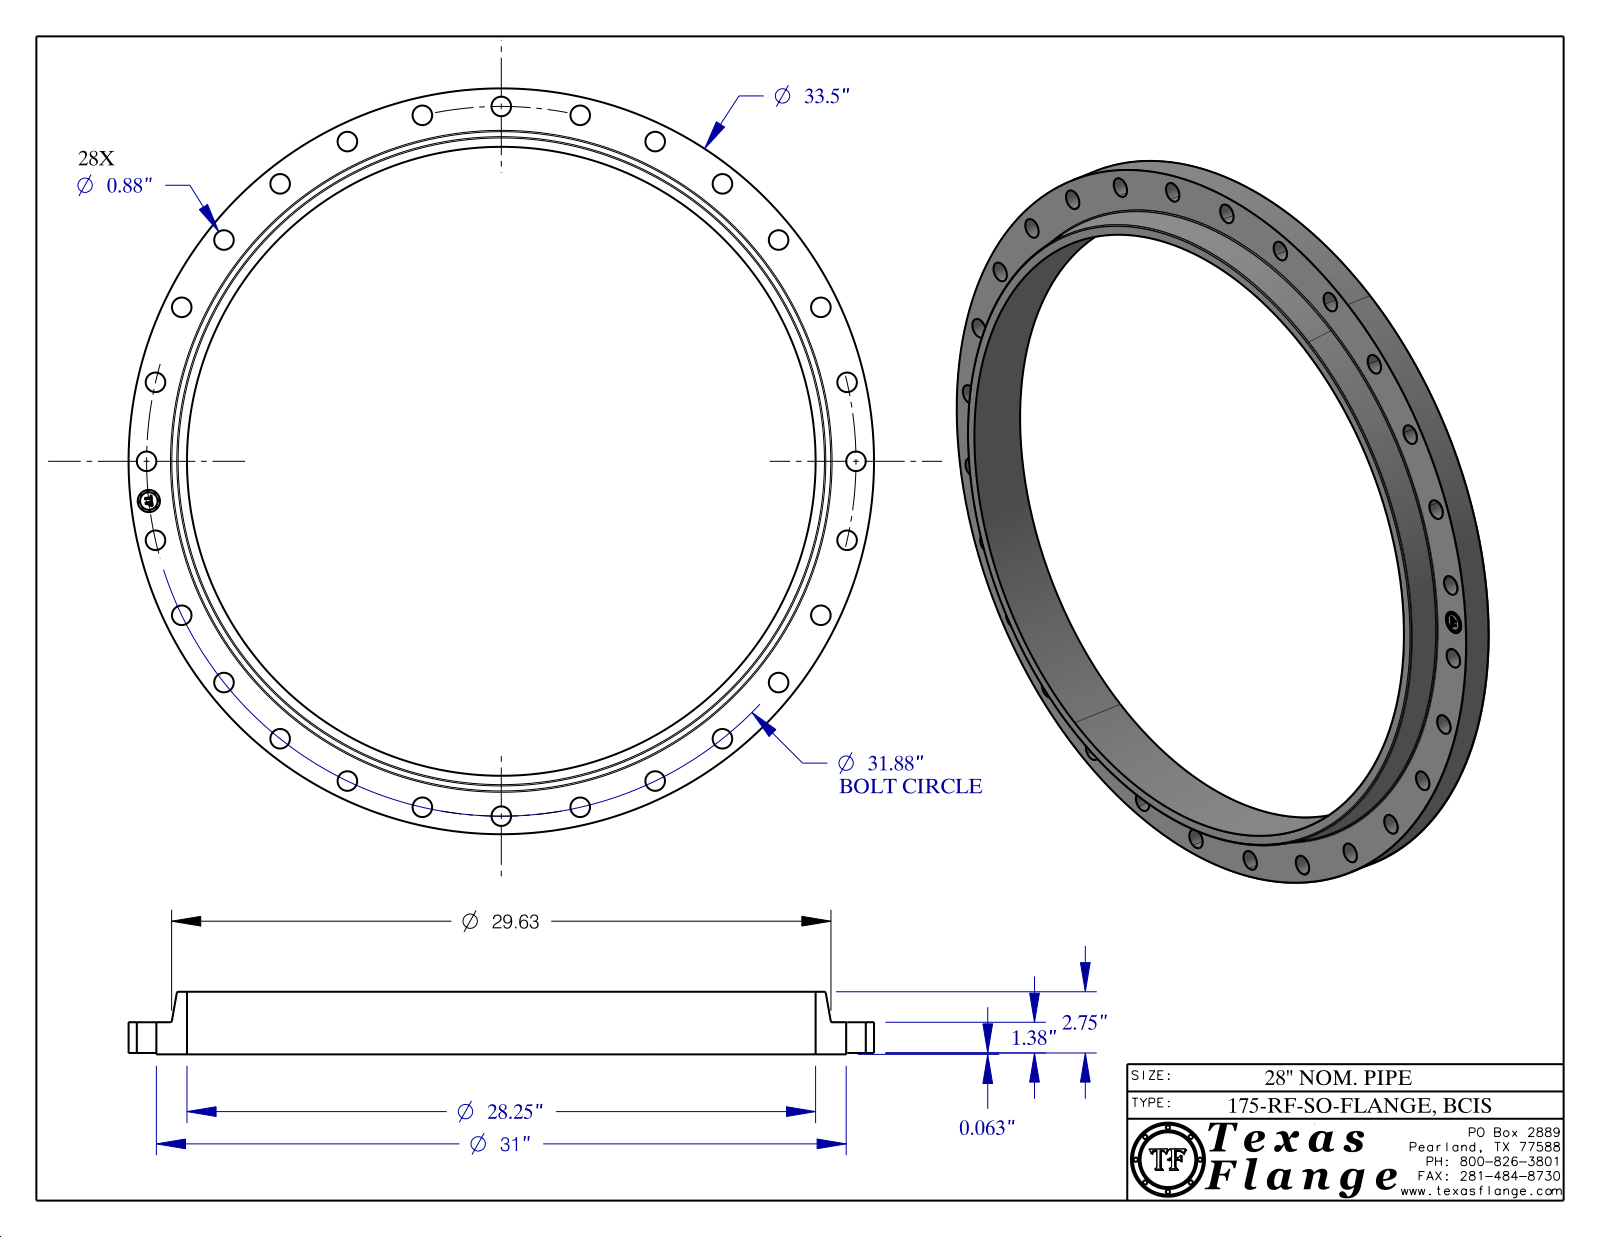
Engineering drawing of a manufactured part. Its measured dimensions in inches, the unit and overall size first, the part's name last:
Units: inches
Overall size (bounding box): 33.5 × 33.5 × 2.813
Round holes (diameter × count): ⌀0.88 ×28, ⌀1 ×1, ⌀28.25 ×1
Round bosses / shafts (diameter × count): ⌀0.061 ×8, ⌀33.5 ×1, ⌀31 ×1, ⌀0.788 ×1
Main face-to-face distances: 1.443, 0.063, 1.38, 2.813, 2.75, 1.37, 0.015, 1.428, 1.365, 1.385
Hole centre spacings: 30.091, 19.877, 24.925, 10.529, 13.832, 31.68, 3.57, 7.094
Volume: 406.5 in³ · Surface area: 1 086 in²
Bodies: 1 solid, 457 faces (369 planar, 82 cylindrical, 6 other)
Part name (STEP PRODUCT): 175-RF-SO
STEP written by: CATIA V5 STEP AP214 (AUTOMOTIVE_DESIGN)
